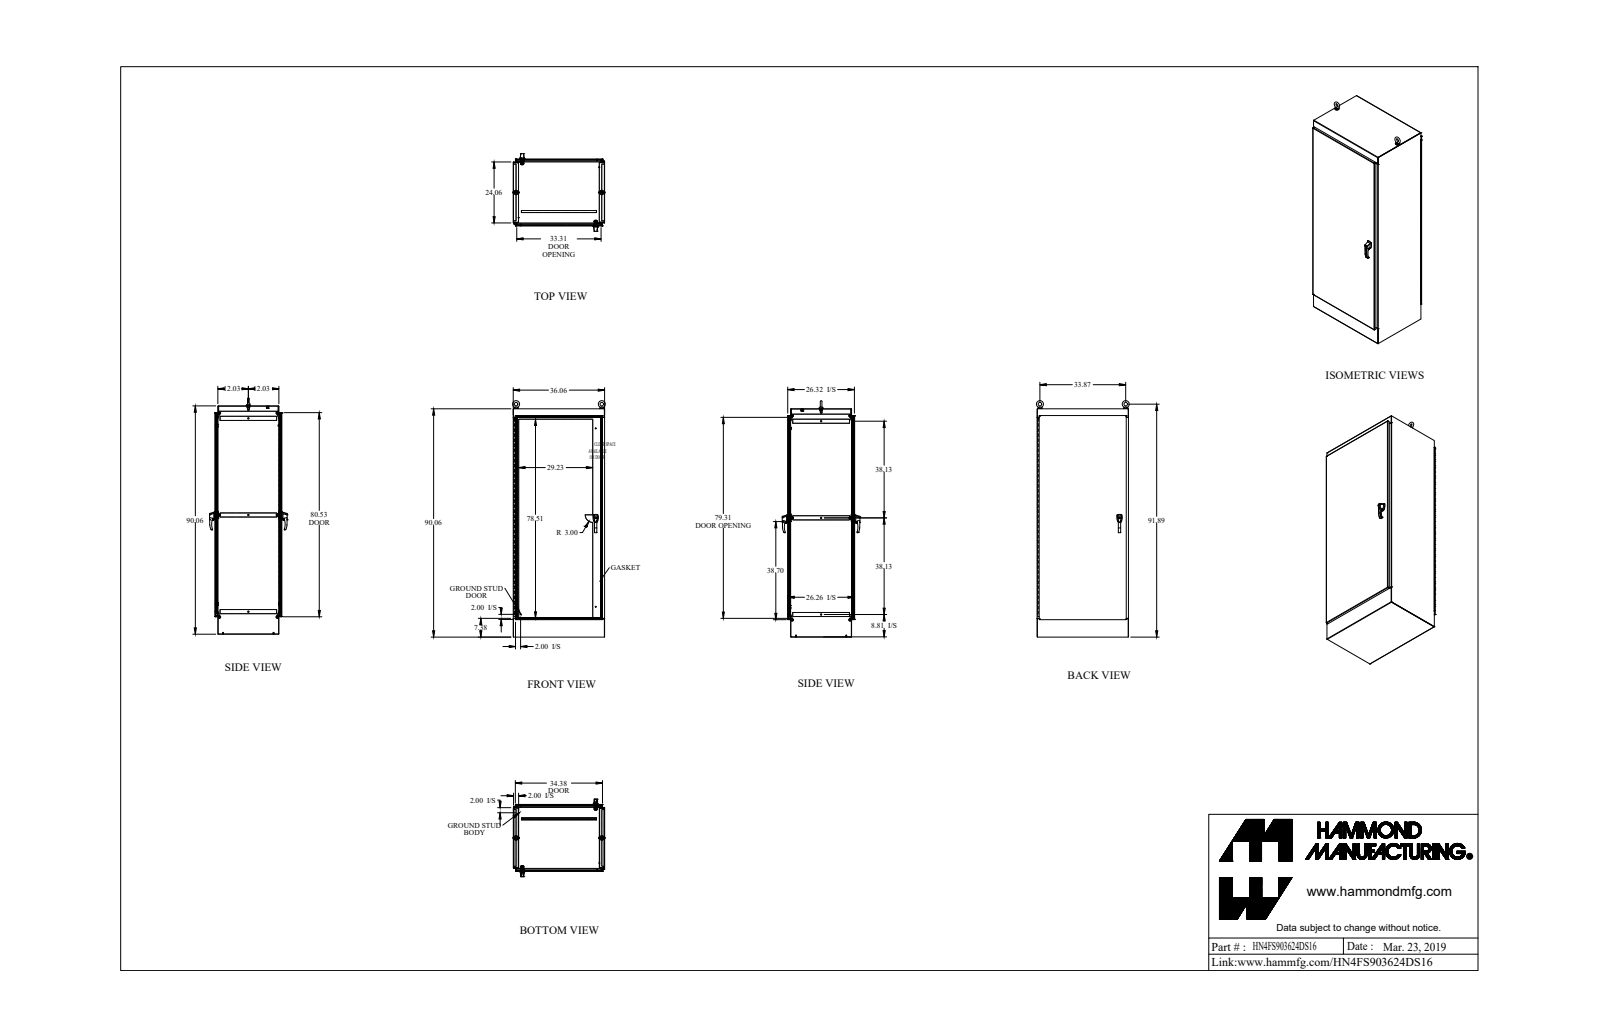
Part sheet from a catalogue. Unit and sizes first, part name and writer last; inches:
Units: inches
Overall size (bounding box): 93.489 × 36.604 × 30.664
Round holes (diameter × count): ⌀0.304 ×26, ⌀0.35 ×8, ⌀0.25 ×5, ⌀0.257 ×4, ⌀0.28 ×4, ⌀0.281 ×4, ⌀0.313 ×4, ⌀0.39 ×4, ⌀0.413 ×4, ⌀0.5 ×3, ⌀0.11 ×2, ⌀0.173 ×2
Round bosses / shafts (diameter × count): ⌀1 ×4, ⌀0.75 ×4, ⌀0.63 ×4, ⌀0.625 ×4, ⌀0.44 ×4, ⌀0.37 ×4, ⌀0.313 ×4, ⌀0.281 ×4
Partial cylindrical surfaces — rounded edges, fillets, slot ends (radius × count): R0.125 ×44, R0.043 ×42, R0.138 ×36, R0.018 ×32, R0.048 ×26, R0.143 ×26, R0.5 ×26, R0.06 ×21
Main face-to-face distances: 0.095, 26.339, 35.965, 26.244, 26.434, 35.87, 1.187, 25.152, 36.06, 89.965
Hole centre spacings: 6, 12, 34.827, 18, 36.344, 38.742, 24, 41.868
Volume: 1 508 in³ · Surface area: 31 944 in²
Bodies: 91 solids, 3764 faces (1646 planar, 1717 cylindrical, 401 other)
Part name (STEP PRODUCT): HN4FS903624DS16
STEP written by: SolidWorks 2018 (AUTOMOTIVE_DESIGN)
